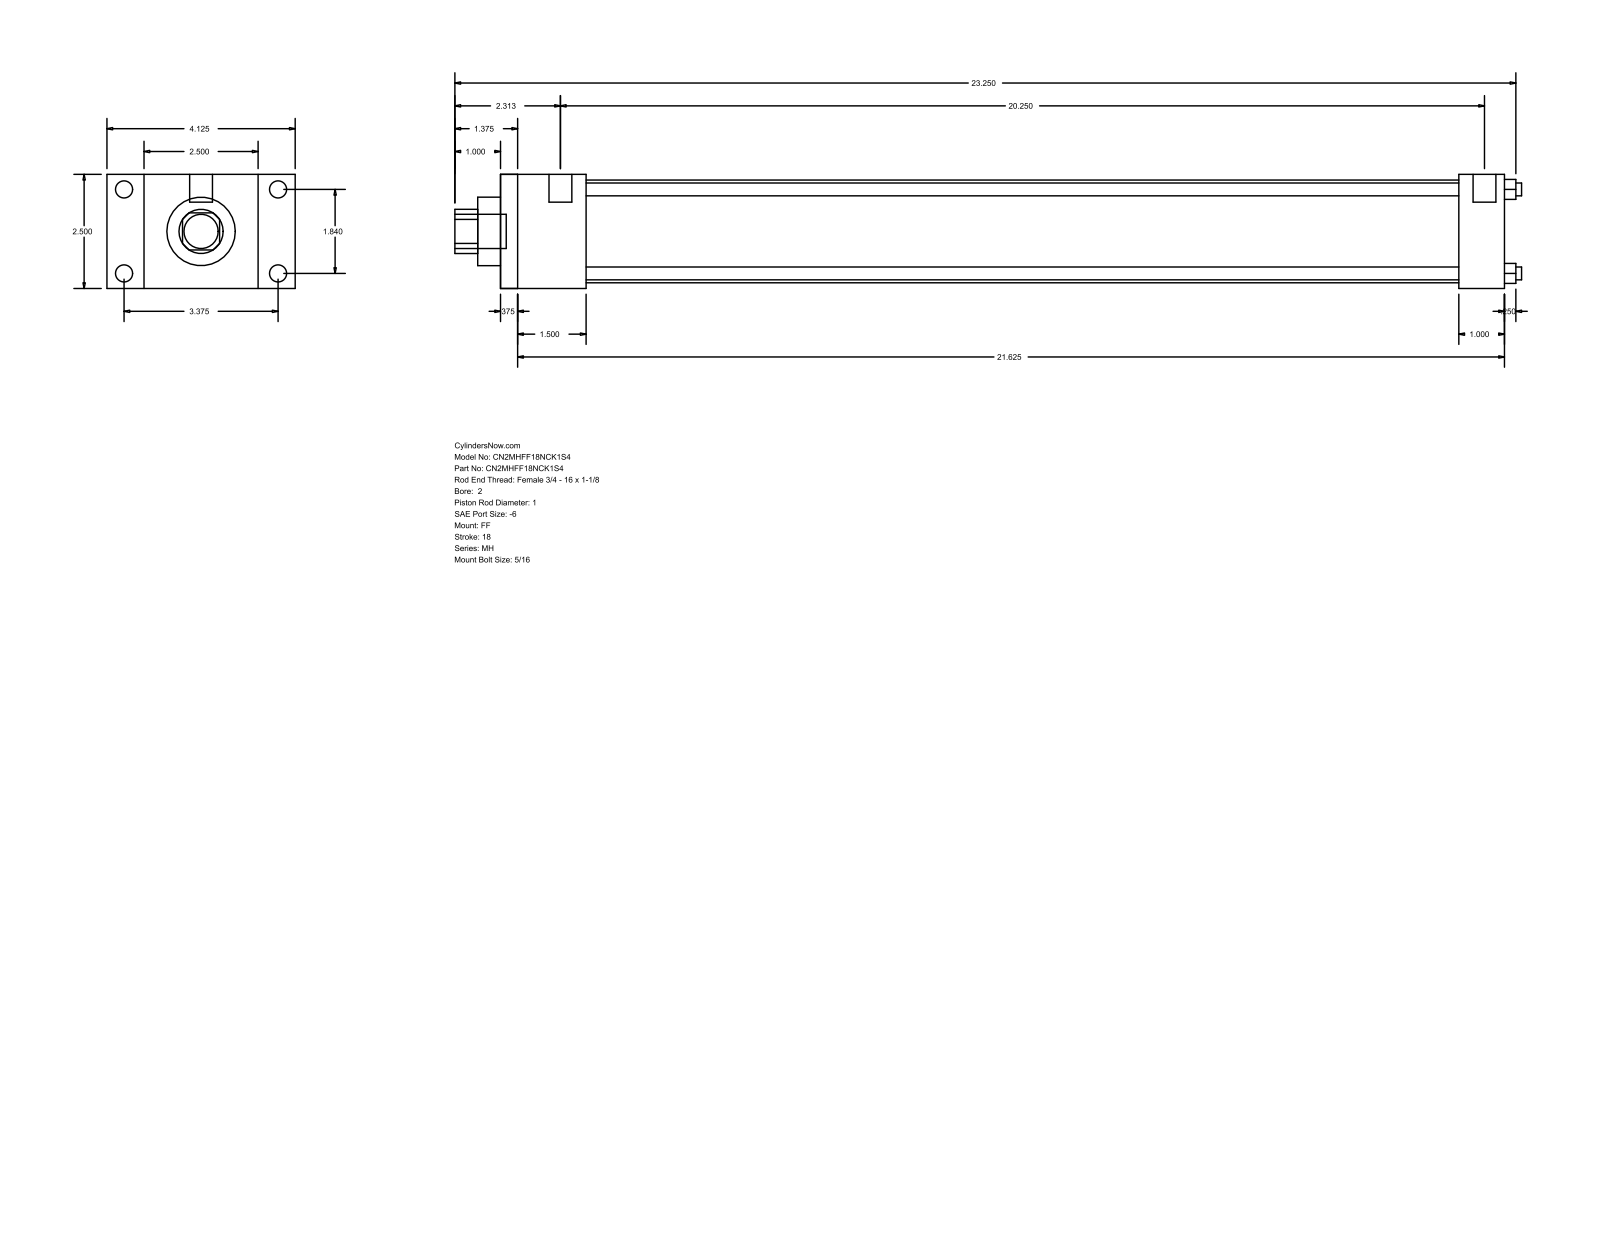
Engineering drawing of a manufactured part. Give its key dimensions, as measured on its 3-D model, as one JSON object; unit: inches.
{"part_name": "MH_FF__0200_1", "step_written_by": "GSSL Pune (CONFIG_CONTROL_DESIGN)", "units": "inches", "bodies": {"solids": 0, "faces": 92, "planar": 64, "cylindrical": 28, "other": 0}, "overall_size": [23.375, 4.125, 2.5], "round_holes": [[0.281, 4], [1, 1], [1.5, 1], [2.25, 1]], "round_bosses_or_shafts": [[0.375, 4], [0.219, 4], [0.5, 2], [0.75, 1]], "partial_cylinders_radius": [[0.484, 1]], "face_to_face_distances": [2.5, 22, 0.375, 21.625, 0.813, 1, 1.875, 21, 1.5, 20.625], "hole_center_spacings": [1.301, 1.84, 2.602]}
